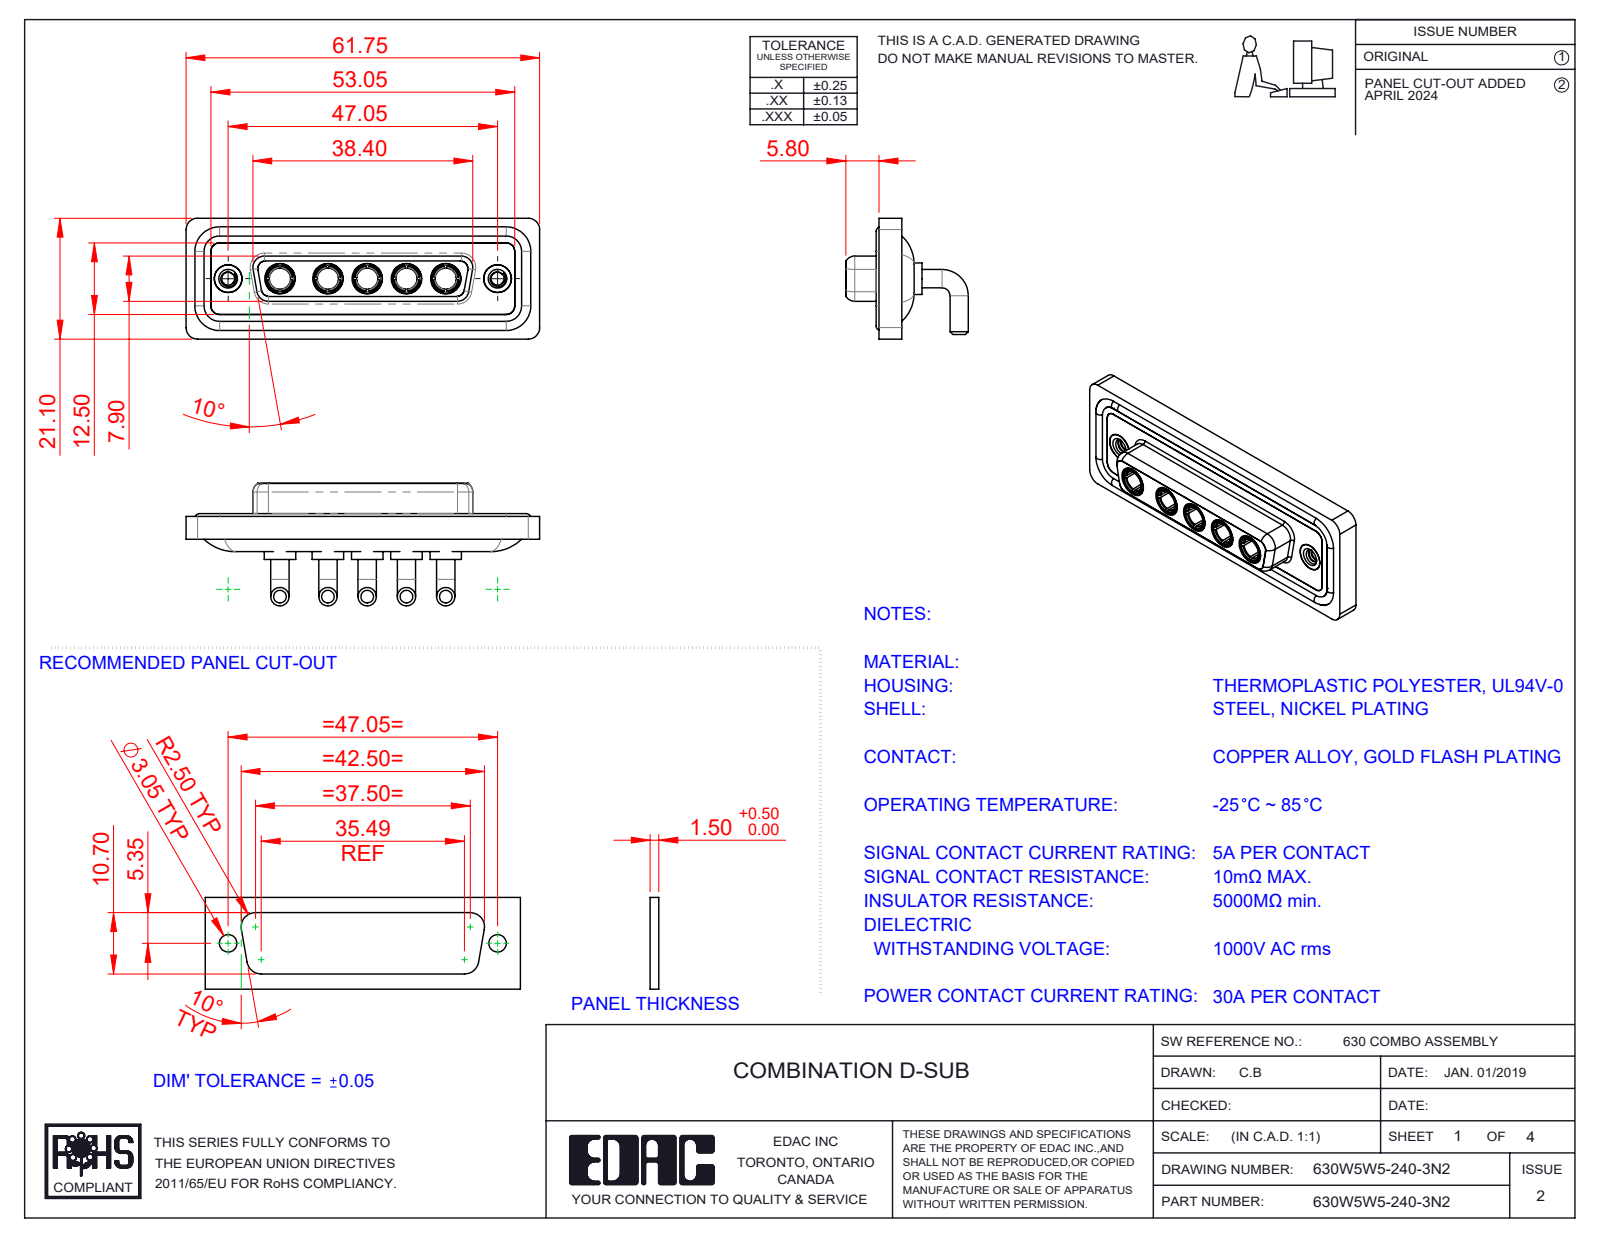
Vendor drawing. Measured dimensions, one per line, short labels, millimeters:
name: Power Socket_30A RA; 630Combo Shell Rear_25 Contacts; 630W5W5-240-3N2; 630Combo Threaded Rivet_2 (+3 more)
written by: SolidWorks 2023 (CONFIG_CONTROL_DESIGN)
unit: mm
bodies: 17 solids, 776 faces (250 planar, 313 cylindrical, 213 other)
size: 61.75 × 21.4 × 21.1
volume: 8 575 mm³; area: 13 905 mm²
holes: 7× ⌀4.85, 5× ⌀3.7, 5× ⌀5.3, 2× ⌀2.26, 2× ⌀4, 2× ⌀4.05, 2× ⌀5
bosses: 10× ⌀3.2, 5× ⌀5.5, 5× ⌀5.2, 5× ⌀4.96, 5× ⌀4.75, 5× ⌀3.75, 4× ⌀1.6, 2× ⌀4.95
rounds: 18× R1.5, 18× R2, 8× R1.35, 8× R1.6, 5× R2.1, 4× R0.25, 4× R0.5, 4× R0.6
face distances: 0.4, 1.8, 4.1, 1.1, 1.5, 2.5, 3.1, 3.7, 1.6, 2.9
hole spacings: 6.86, 9.04, 38.01, 6.87, 8.38, 13.72, 13.73, 15.25
